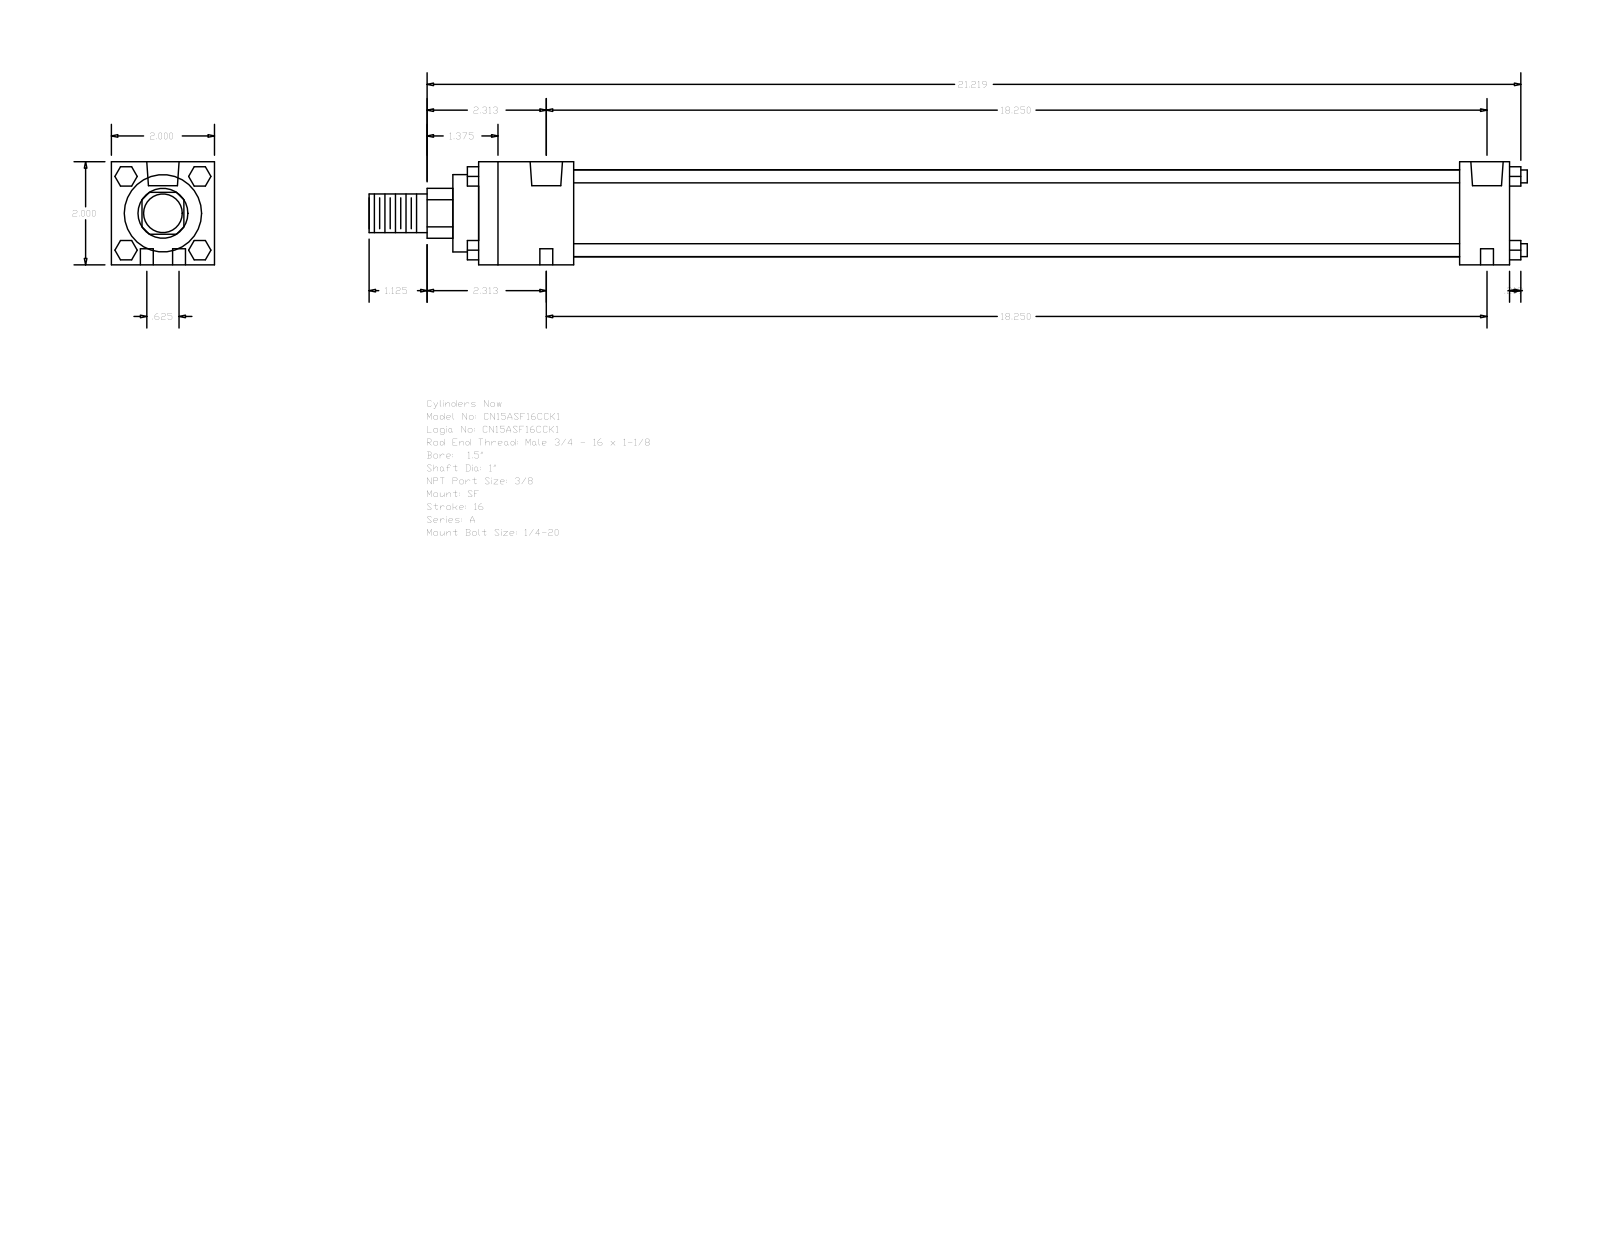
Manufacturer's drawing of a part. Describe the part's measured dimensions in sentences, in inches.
The part is named "A_SF__0150_1". Its 3-D file was written by "GSSL Pune (CONFIG_CONTROL_DESIGN)". It is 0 solids with 124 faces: 94 planar, 30 cylindrical and 0 other. Overall it measures 22.469 by 2 by 2 inches. Round holes: 4 of diameter 0.25, 2 of diameter 0.219, 2 of diameter 0.627. Round bosses or shafts: 4 of diameter 0.25, 1 of diameter 1.69, 1 of diameter 1.5, 1 of diameter 1, 1 of diameter 0.75. Partial cylindrical surfaces (rounded edges, fillets, slot ends): 1 of radius 0.484. The main face-to-face distances are 2, 20, 1.844, 19.031, 17.187, 18.156, 0.969, 0.5, 2.344, 19.531. The hole center spacings are 0.313, 18.253, 18.25, 0.625, 18.261, 17.937.
